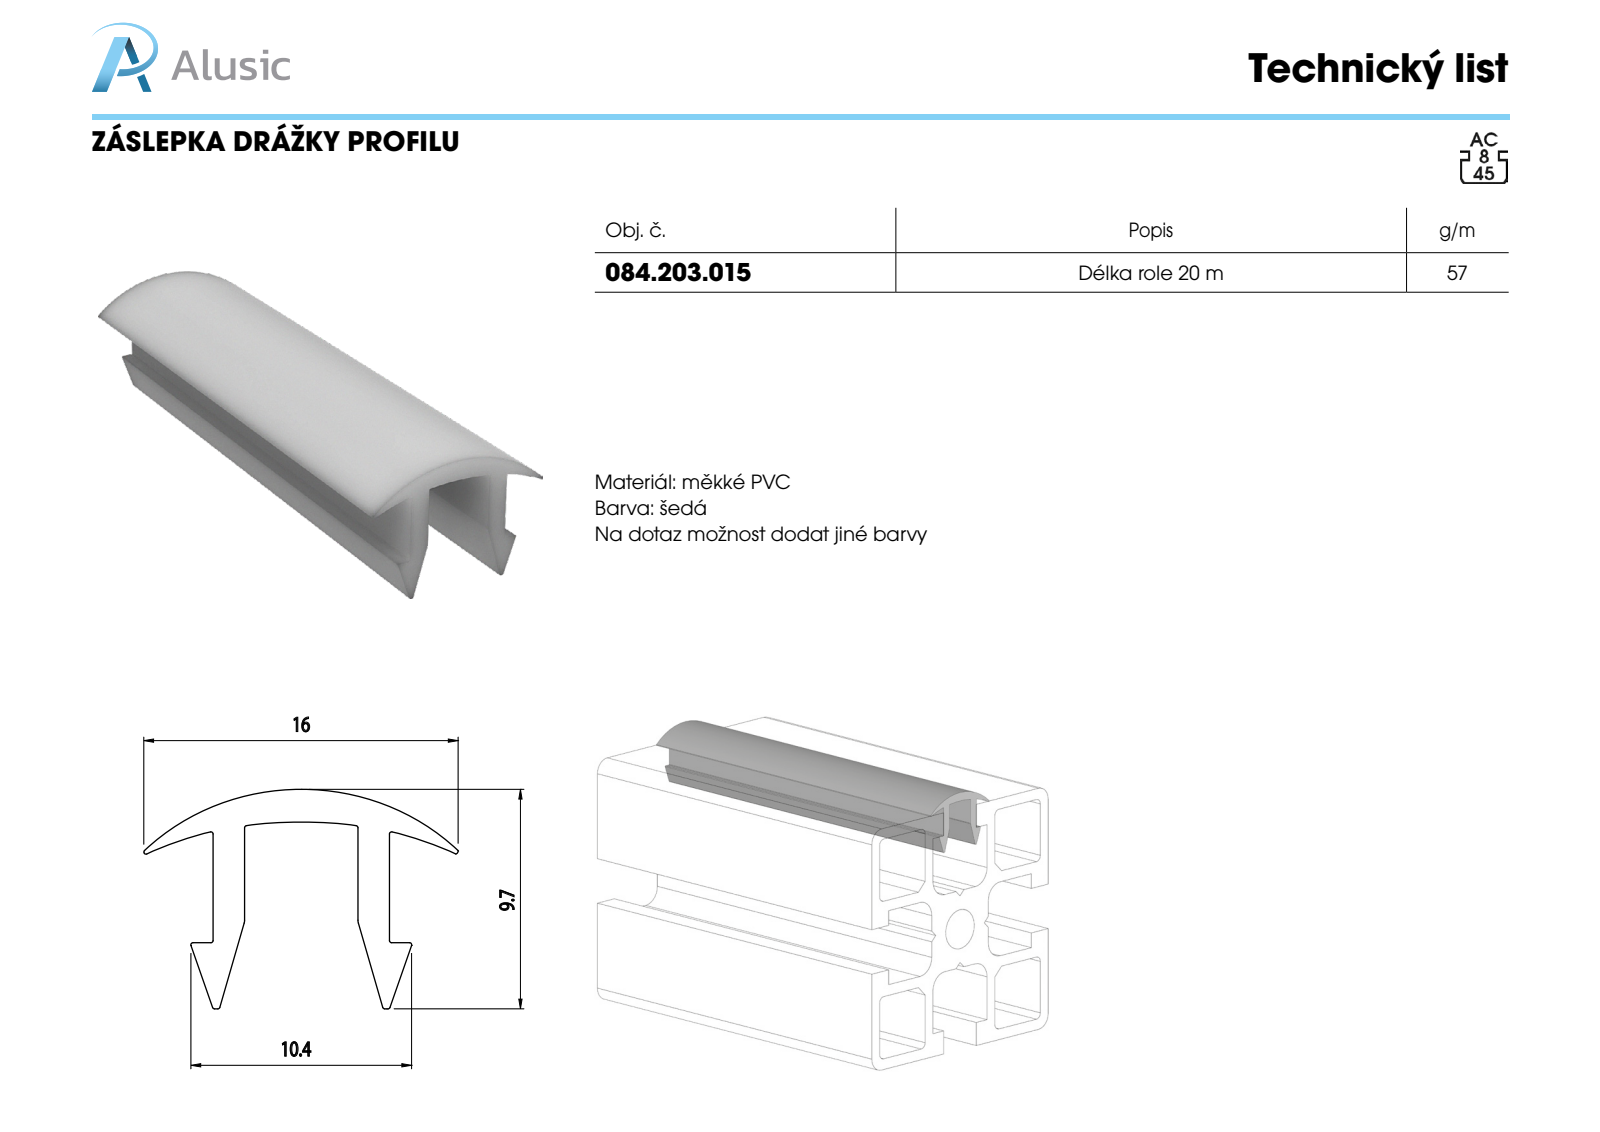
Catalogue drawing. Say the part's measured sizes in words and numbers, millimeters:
The part is named "084.203.015". Its 3-D file was written by "SolidWorks 2011 (CONFIG_CONTROL_DESIGN)". It is 1 solid with 38 faces: 14 planar, 24 cylindrical and 0 other. Overall it measures 100 by 15 by 10.45 millimeters. Its volume is 4 129 cubic millimeters and its surface area 6 717 square millimeters. Partial cylindrical surfaces (rounded edges, fillets, slot ends): 14 of radius 0.1, 2 of radius 0.5, 2 of radius 16.78, 1 of radius 11.02, 1 of radius 20.25. The main face-to-face distances are 1.5, 6.9, 8.4, 5.4, 100, 3.15.
